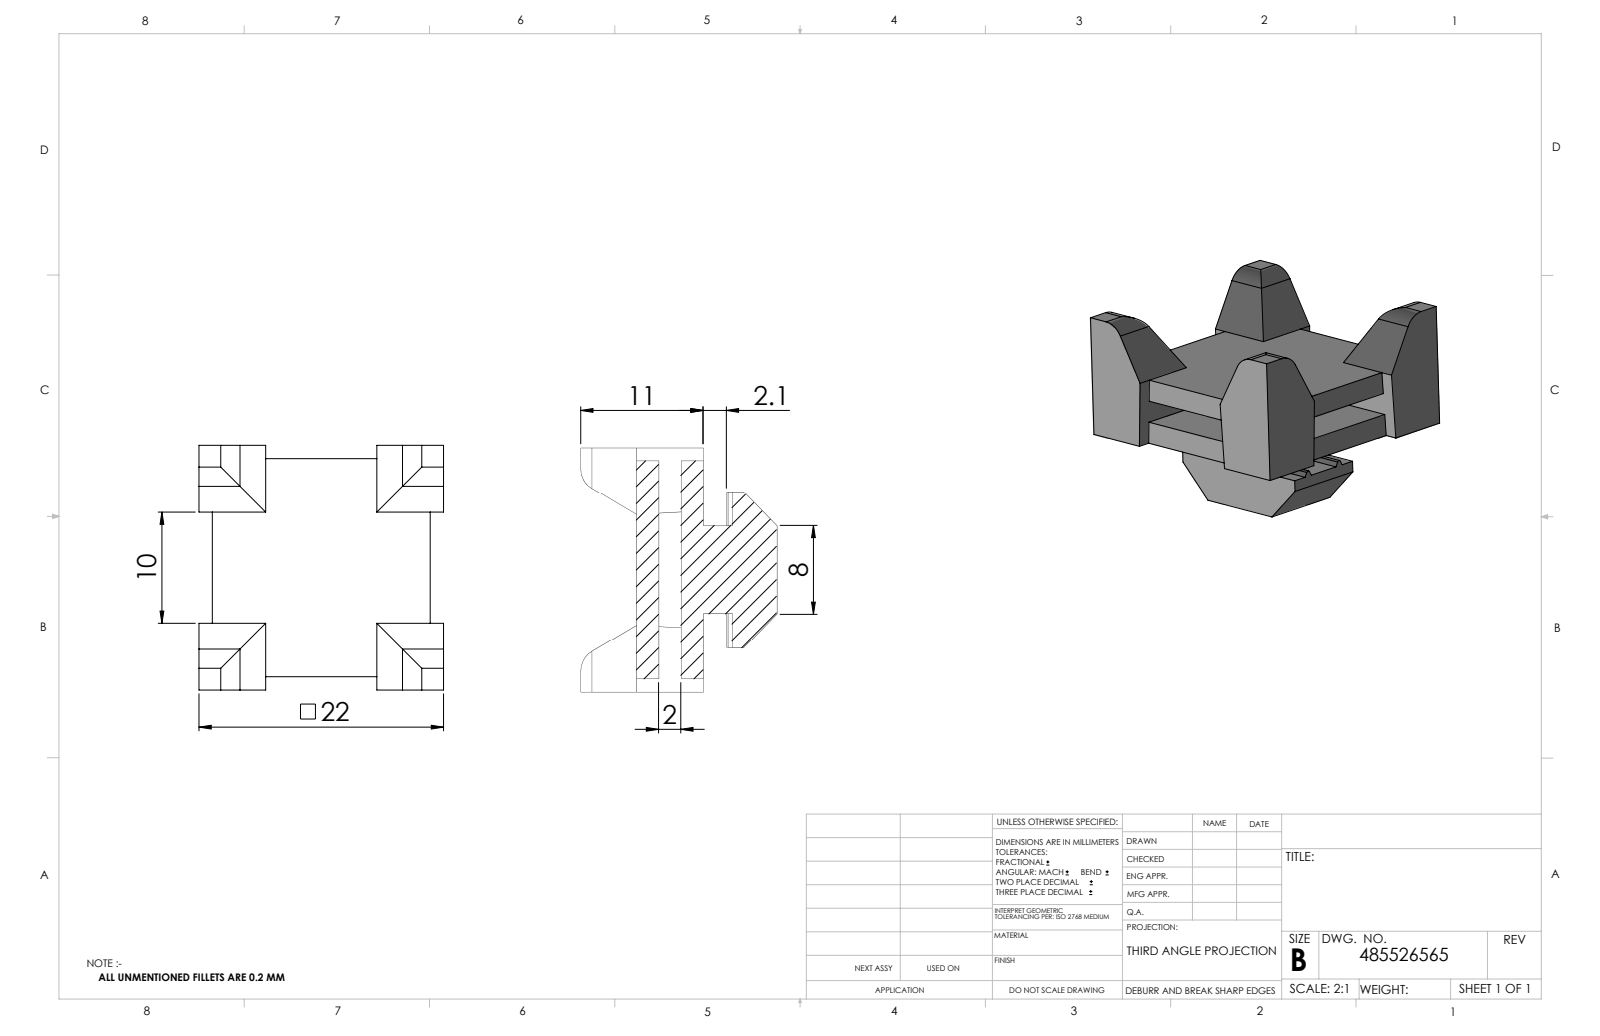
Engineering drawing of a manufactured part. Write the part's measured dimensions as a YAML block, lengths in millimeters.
part_name: "485526565_c_1"
step_written_by: "SolidWorks 2014 (CONFIG_CONTROL_DESIGN)"
units: millimeters
bodies: {solids: 1, faces: 77, planar: 63, cylindrical: 14, other: 0}
overall_size: [22, 22, 17.6]
volume: 2913
surface_area: 2641
partial_cylinders:
  - {radius: 2, count: 4}
  - {radius: 0.2, count: 2}
  - {radius: 3.5, count: 2}
face_to_face_distances: [2, 4, 6, 22, 1.2, 20.8, 6.6, 8.6, 7.25, 14.75]
